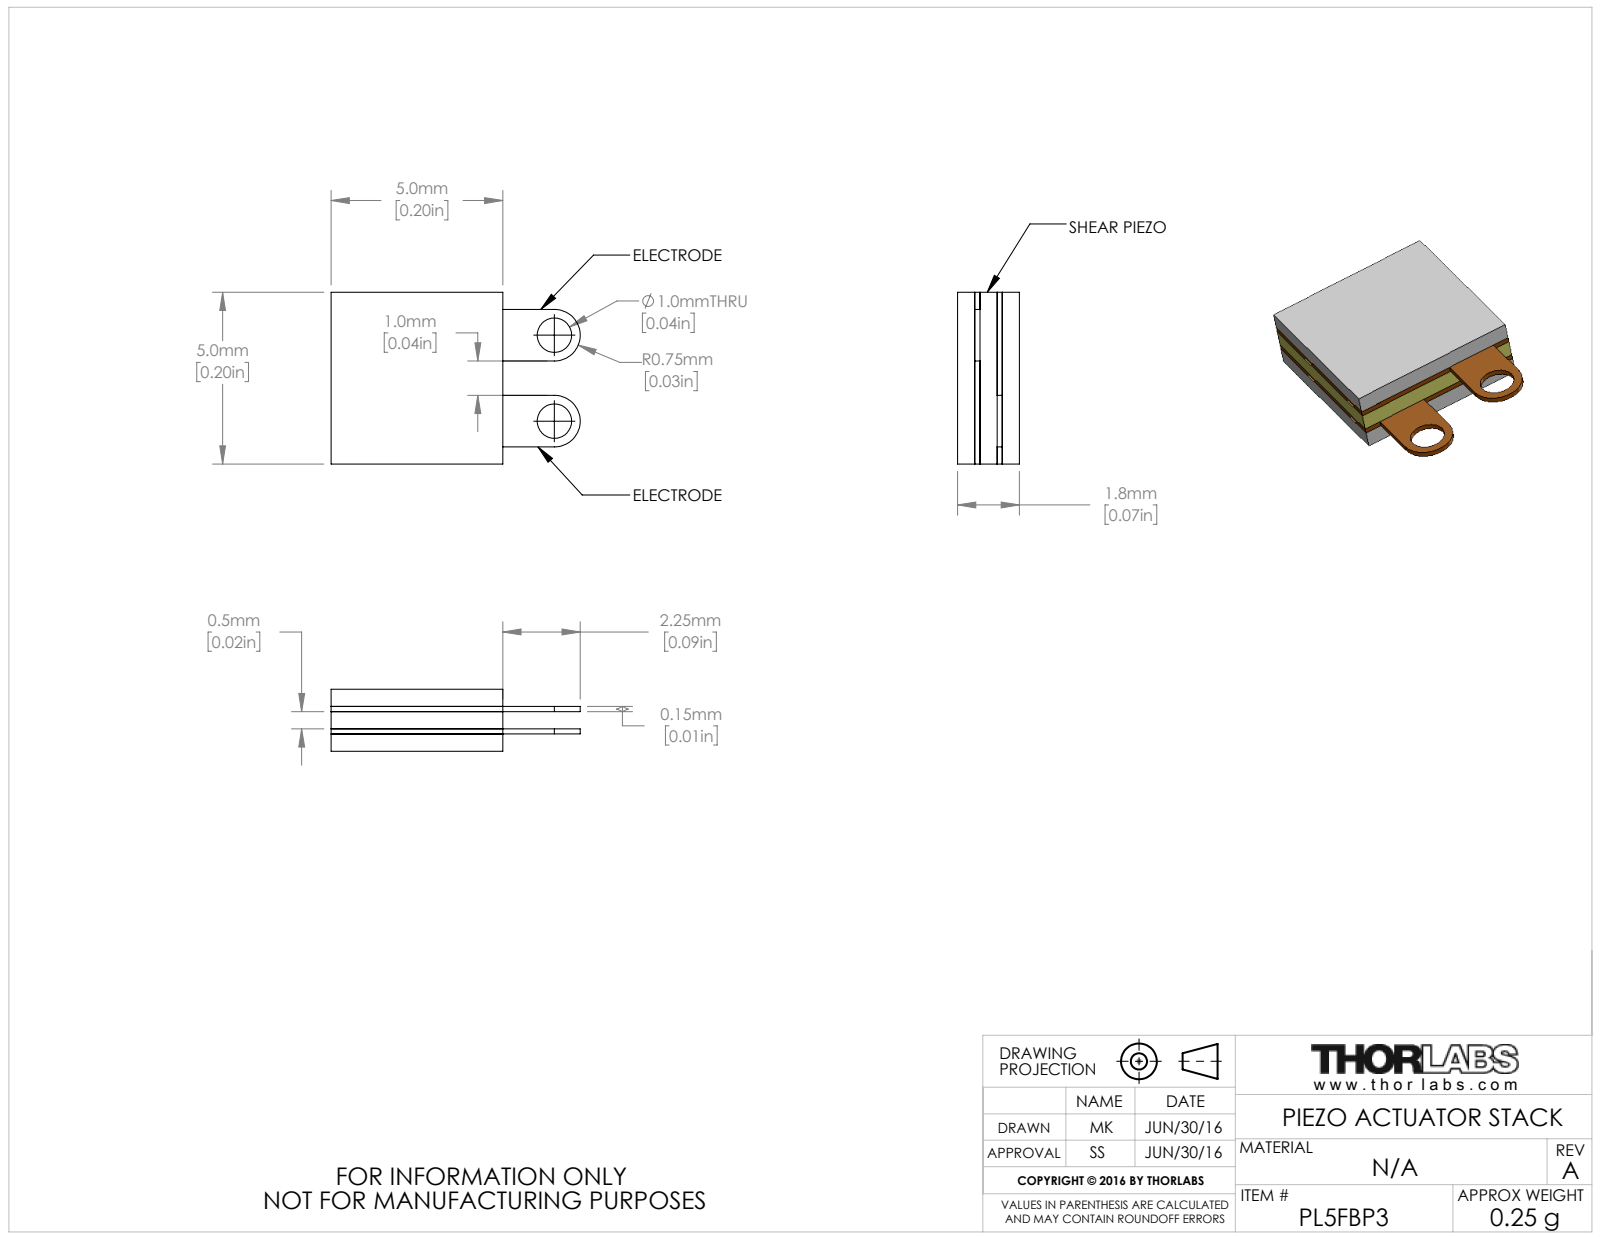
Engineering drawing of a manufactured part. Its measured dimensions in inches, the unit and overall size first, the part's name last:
Units: inches
Overall size (bounding box): 0.285 × 0.197 × 0.071
Round holes (diameter × count): ⌀0.039 ×2
Partial cylindrical surfaces — rounded edges, fillets, slot ends (radius × count): R0.03 ×2
Main face-to-face distances: 0.026, 0.02, 0.031, 0.045, 0.051, 0.071, 0.197, 0.079, 0.118, 0.177
Hole centre spacings: 0.098
Volume: 0.003 in³ · Surface area: 0.46 in²
Bodies: 5 solids, 42 faces (36 planar, 6 cylindrical, 0 other)
Part name (STEP PRODUCT): CTN009239
STEP written by: SolidWorks 2016 (AUTOMOTIVE_DESIGN)
